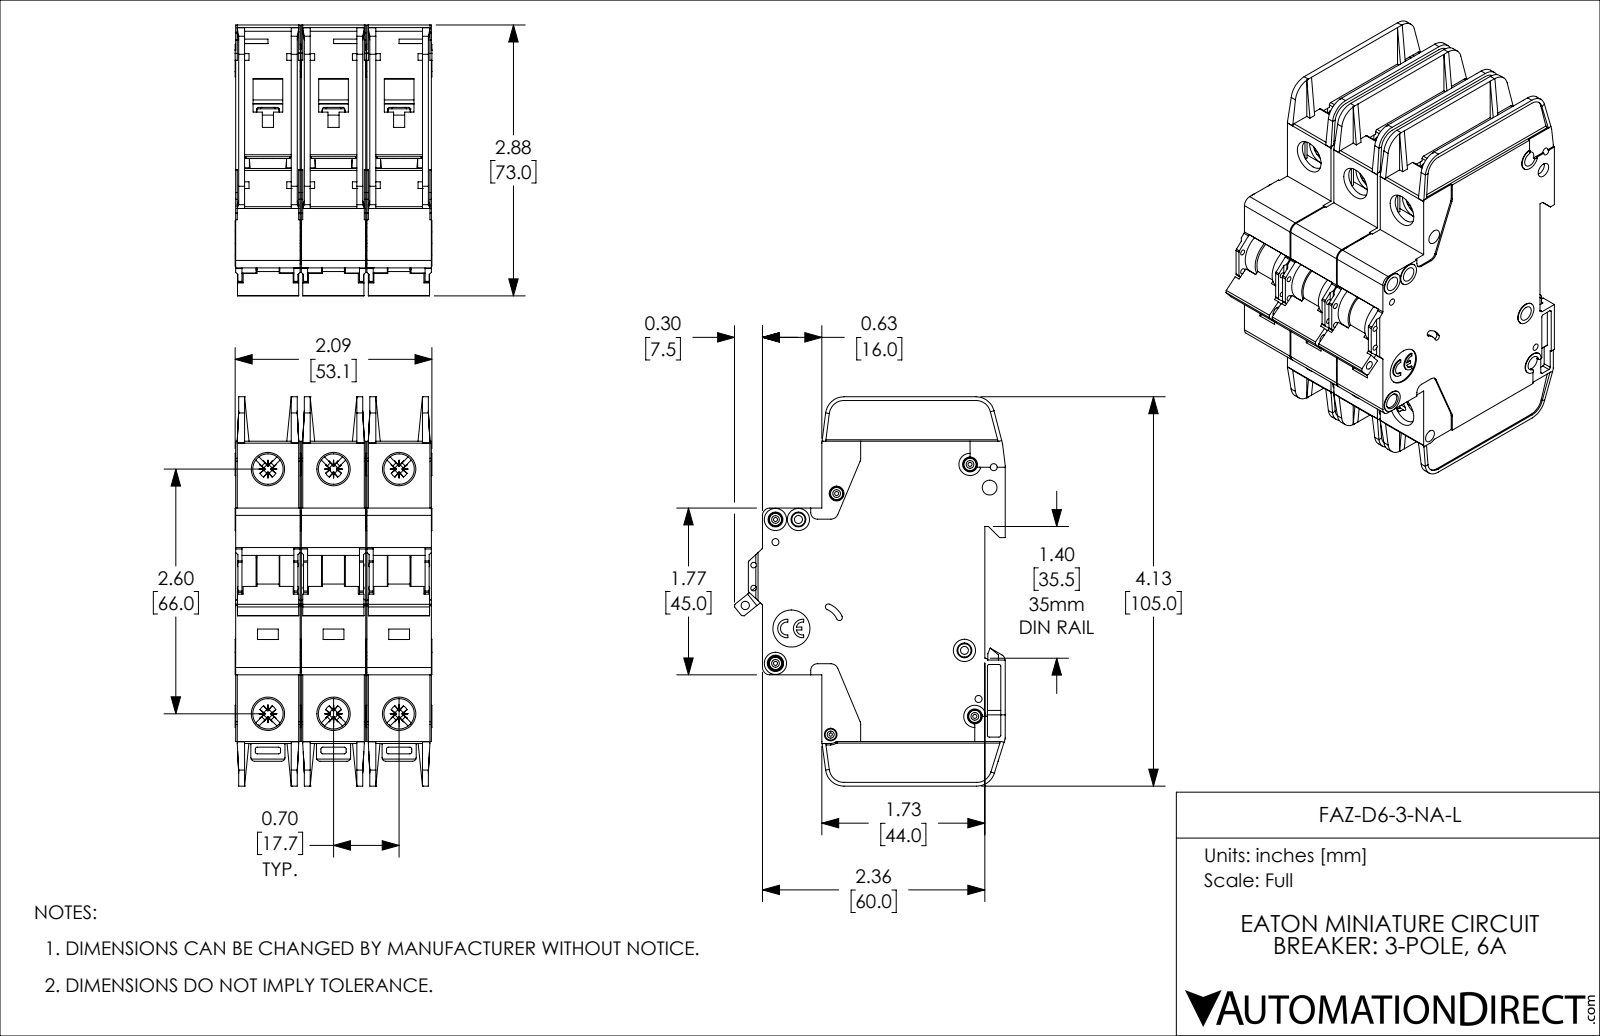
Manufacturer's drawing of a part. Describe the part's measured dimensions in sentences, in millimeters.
The part is named "FAZ-D6-3-NA-L". Its 3-D file was written by "SolidWorks 2019 (AUTOMOTIVE_DESIGN)". It is 3 solids with 3381 faces: 2013 planar, 1071 cylindrical and 297 other. Overall it measures 105 by 73.1 by 53.1 millimeters. Its volume is 230 200 cubic millimeters and its surface area 79 350 square millimeters. Round holes: 8 of diameter 4, 6 of diameter 8.2, 5 of diameter 1.1, 4 of diameter 1.9, 2 of diameter 1.5, 2 of diameter 2.2, 1 of diameter 0.9, 1 of diameter 2.3, 1 of diameter 2.5, 1 of diameter 3.4, 1 of diameter 10. Round bosses or shafts: 5 of diameter 3.3, 4 of diameter 6, 4 of diameter 3, 3 of diameter 2.5. Partial cylindrical surfaces (rounded edges, fillets, slot ends): 72 of radius 0.5, 30 of radius 0.4, 18 of radius 1, 12 of radius 1.1, 12 of radius 2, 6 of radius 0.2, 6 of radius 0.3, 6 of radius 0.7. The main face-to-face distances are 17.7, 1.2, 35.4, 17.4, 15, 35.1, 18.9, 16.5, 2.7, 2.4. The hole center spacings are 17.7, 68.3, 66, 6.2, 13.6, 22.1, 35.4, 74.9.
